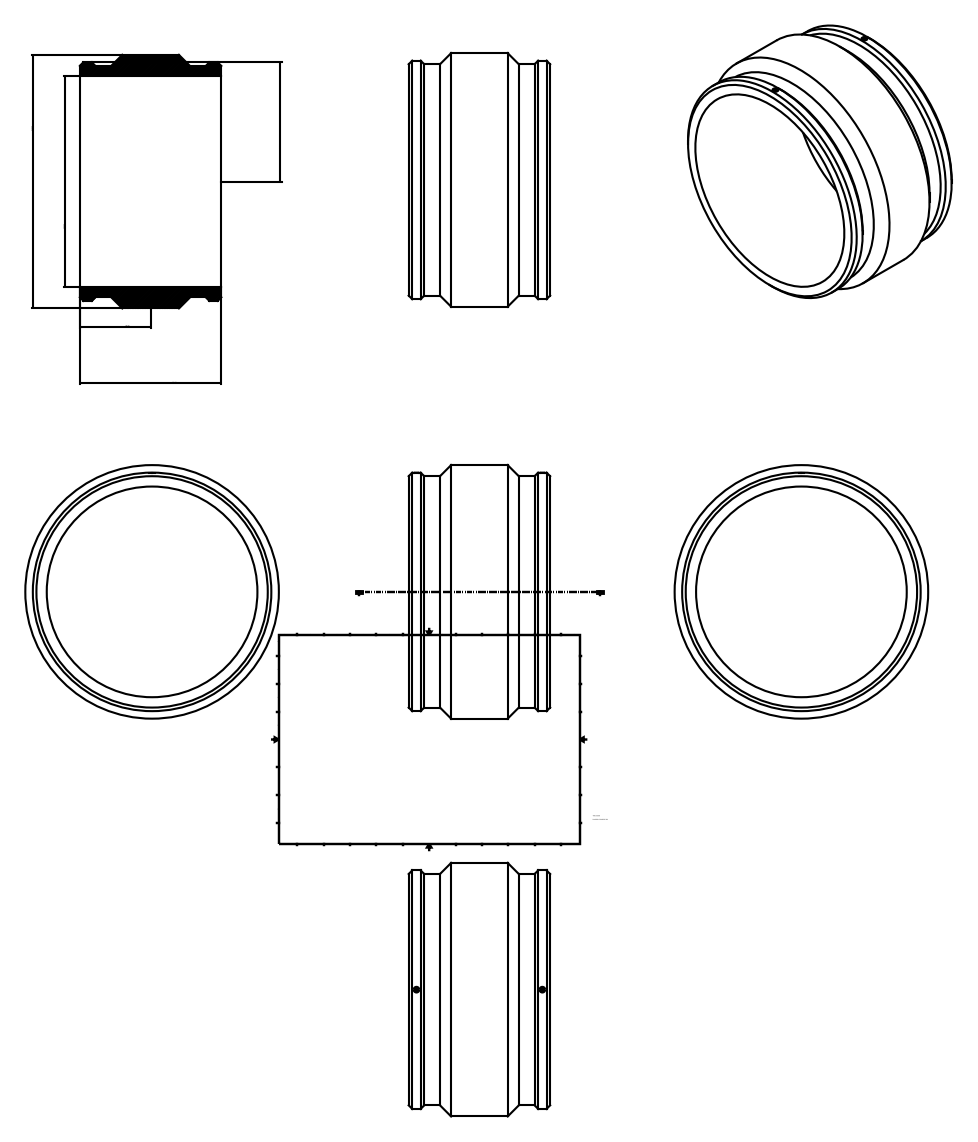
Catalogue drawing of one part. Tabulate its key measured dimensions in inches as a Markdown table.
| quantity | value |
| --- | --- |
| part name | 490103560 |
| STEP written by | Autodesk Inventor 2015 (AUTOMOTIVE_DESIGN) |
| units | inches |
| bodies | 1 solid, 28 faces (8 planar, 14 cylindrical, 6 other) |
| overall size | 26.535 × 26.535 × 14.803 |
| volume | 1 891 in³ |
| surface area | 2 492 in² |
| round holes (diameter × count) | 0.394 × 2, 22.047 × 1 |
| round bosses / shafts (diameter × count) | 0.591 × 2, 0.157 × 2, 26.535 × 1, 24.961 × 1, 24.212 × 1 |
| main face-to-face distances | 14.803, 0.551, 0.433, 0.118 |
| hole center spacings | 13.175 |
